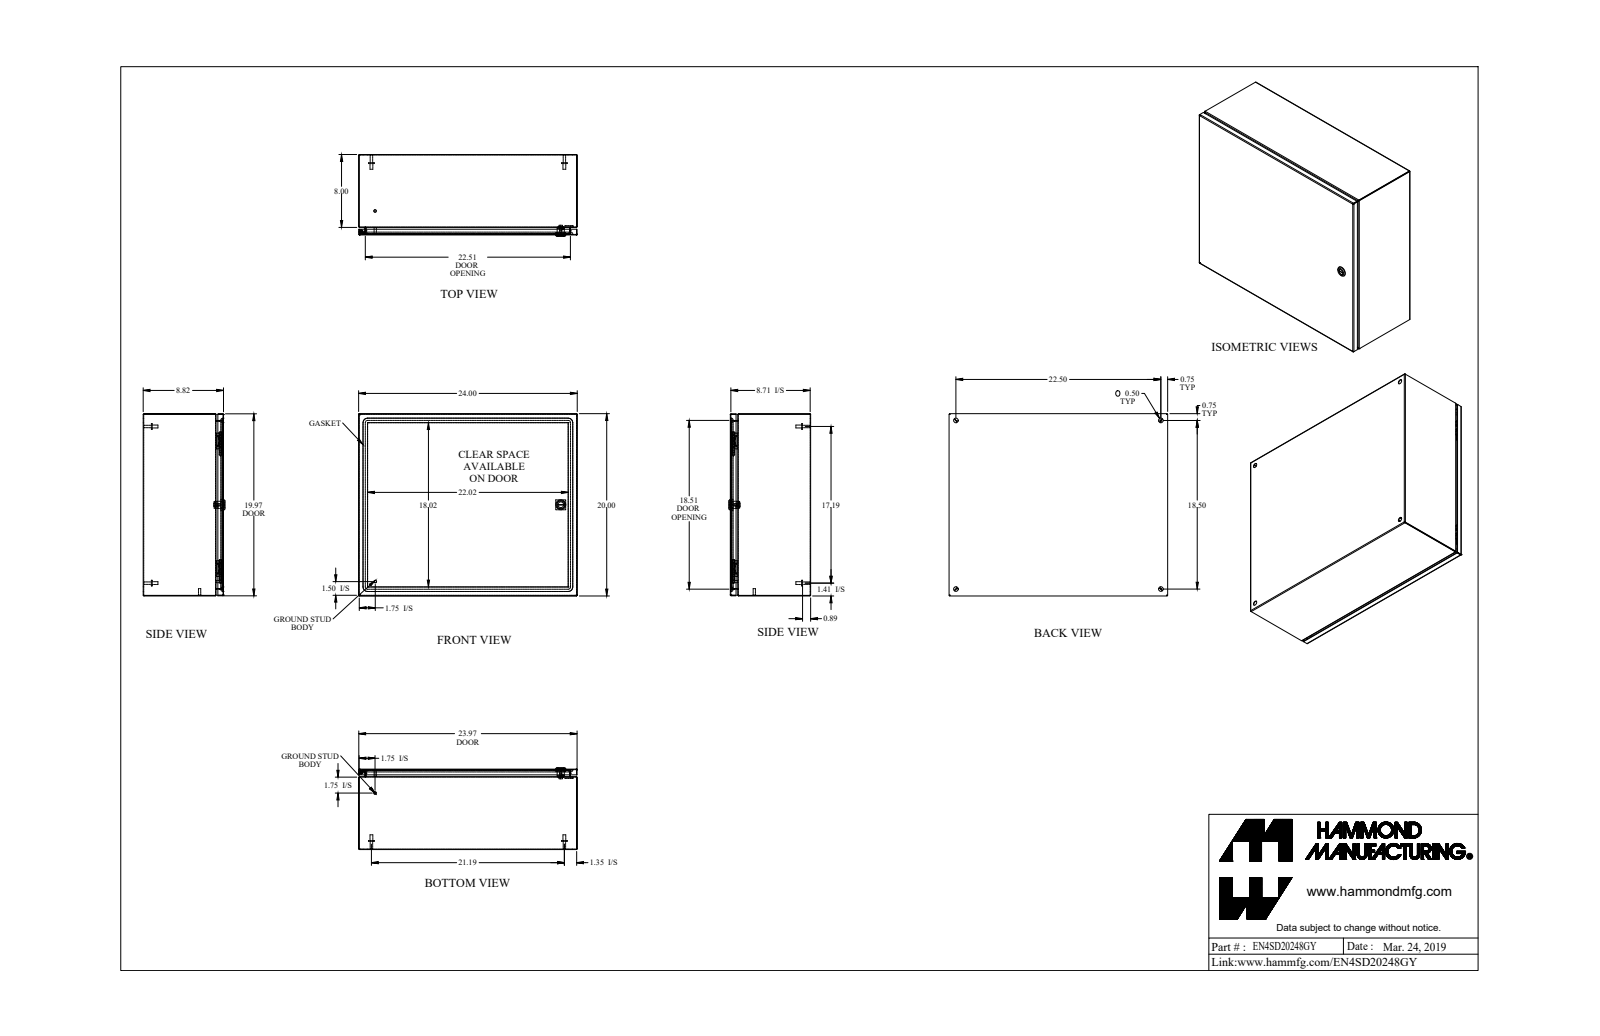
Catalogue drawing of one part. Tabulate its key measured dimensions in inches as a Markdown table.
| quantity | value |
| --- | --- |
| part name | EN4SD20248GY_Default |
| STEP written by | SolidWorks 2019 (CONFIG_CONTROL_DESIGN) |
| units | inches |
| bodies | 21 solids, 634 faces (285 planar, 213 cylindrical, 136 other) |
| overall size | 24 × 20 × 8.982 |
| volume | 113.2 in³ |
| surface area | 3 865 in² |
| round holes (diameter × count) | 0.5 × 4, 0.172 × 1, 0.232 × 1, 0.24 × 1, 0.242 × 1, 0.625 × 1, 0.785 × 1 |
| round bosses / shafts (diameter × count) | 0.625 × 4, 0.313 × 4, 0.27 × 4, 0.281 × 2, 0.25 × 2, 1.1 × 1, 0.525 × 1, 0.455 × 1 |
| partial cylindrical surfaces (radius × count) | 0.029 × 21, 0.086 × 21, 0.25 × 16, 19 × 8, 0.006 × 4, 0.062 × 4, 0.499 × 4, 0.125 × 2 |
| main face-to-face distances | 0.057, 8.765, 8.708, 8.822, 19.943, 23.943, 19.886, 20, 23.886, 24 |
| hole center spacings | 18.5, 22.5, 23.351, 29.129, 9.31, 9.311 |
